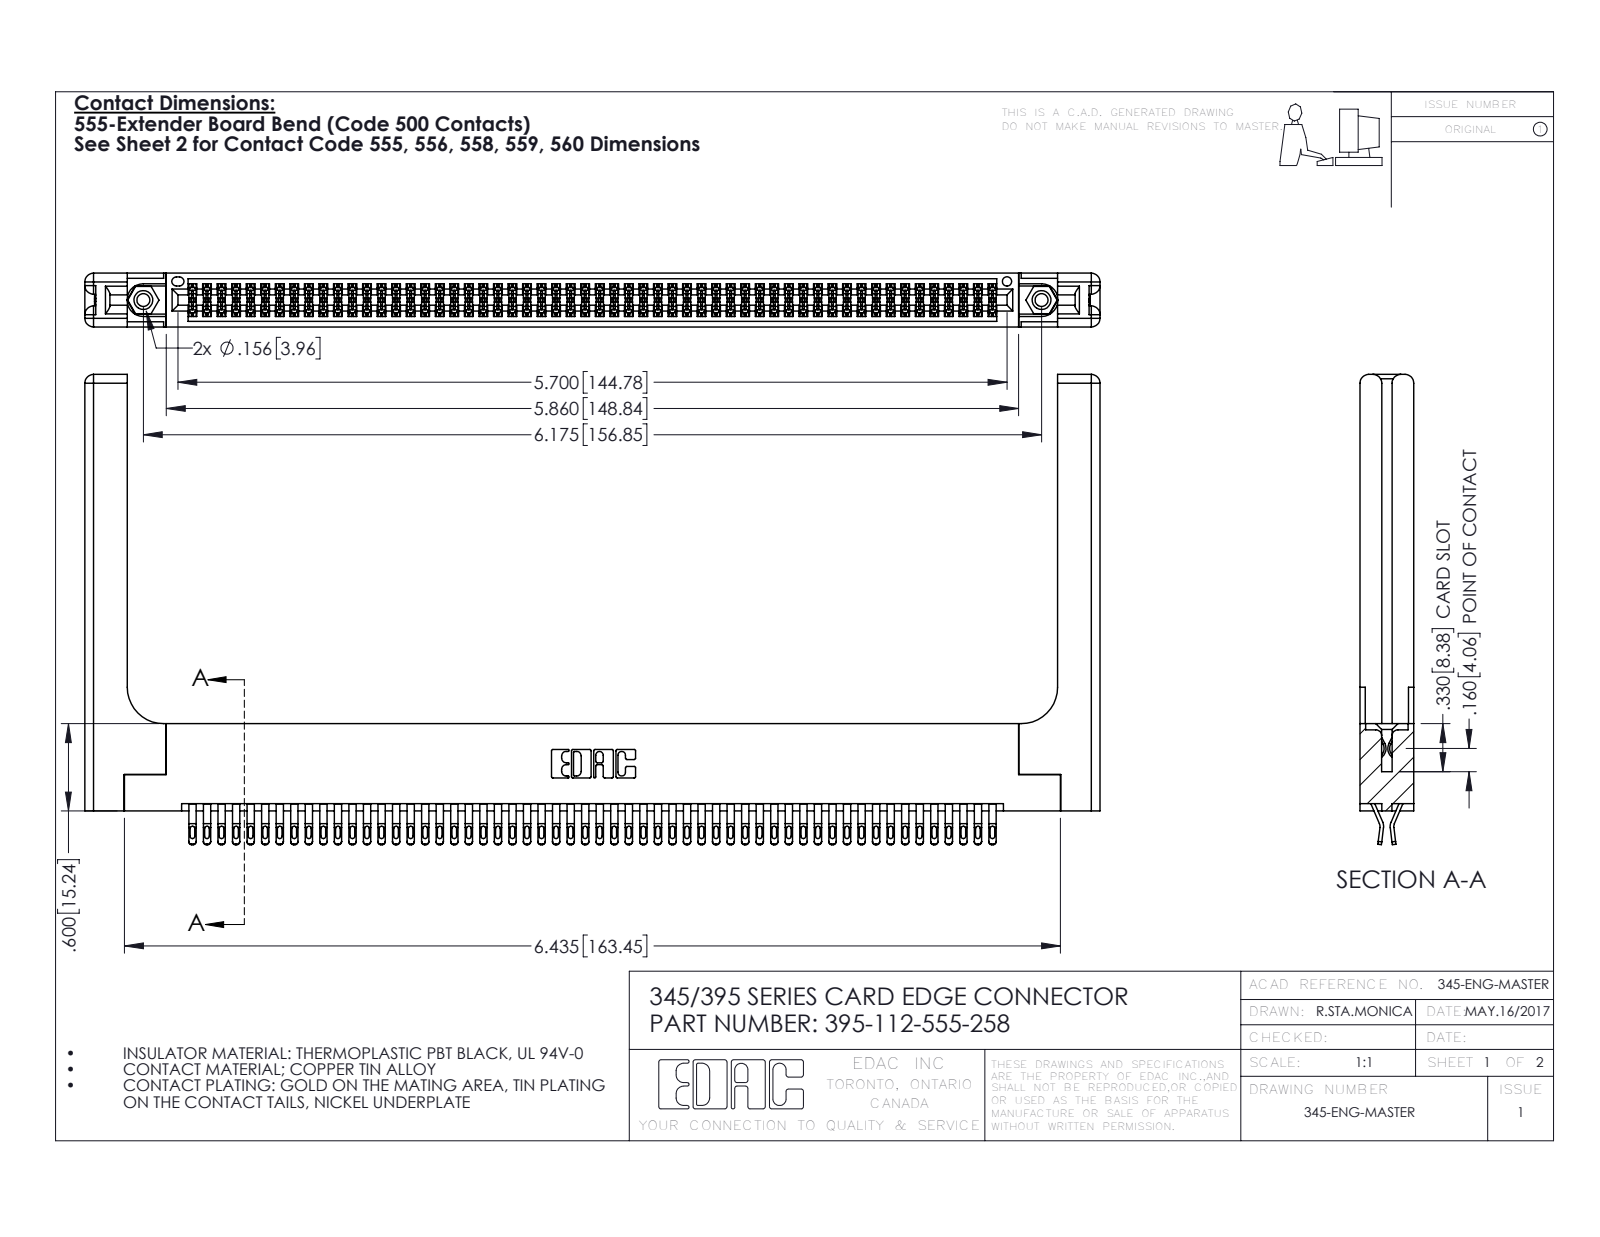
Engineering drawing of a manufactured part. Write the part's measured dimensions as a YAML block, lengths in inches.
part_name: "345-292-001_555 Tail; 395-112-555-258; 345 Part_Flush Mounting Lugs - 0.156 Dia-TH; 345-250-001_345-250-001-102 (+1 more)"
step_written_by: "SolidWorks 2016 (CONFIG_CONTROL_DESIGN)"
units: inches
bodies: {solids: 117, faces: 6654, planar: 3700, cylindrical: 2894, other: 60}
overall_size: [6.979, 3.232, 0.37]
volume: 1.596
surface_area: 50.51
round_holes:
  - {diameter: 0.089, count: 2}
  - {diameter: 0.125, count: 2}
  - {diameter: 0.156, count: 2}
  - {diameter: 0.064, count: 1}
round_bosses_or_shafts:
  - {diameter: 0.155, count: 2}
partial_cylinders:
  - {radius: 0.016, count: 280}
  - {radius: 0.02, count: 224}
  - {radius: 0.006, count: 168}
  - {radius: 0.01, count: 22}
  - {radius: 0.06, count: 16}
  - {radius: 0.007, count: 6}
  - {radius: 0.031, count: 6}
  - {radius: 0.026, count: 3}
face_to_face_distances: [0.072, 0.298, 0.37, 0.025, 0.2, 0.098, 0.272, 0.225, 0.148, 0.15]
hole_center_spacings: [0.27, 5.939, 6.175]
